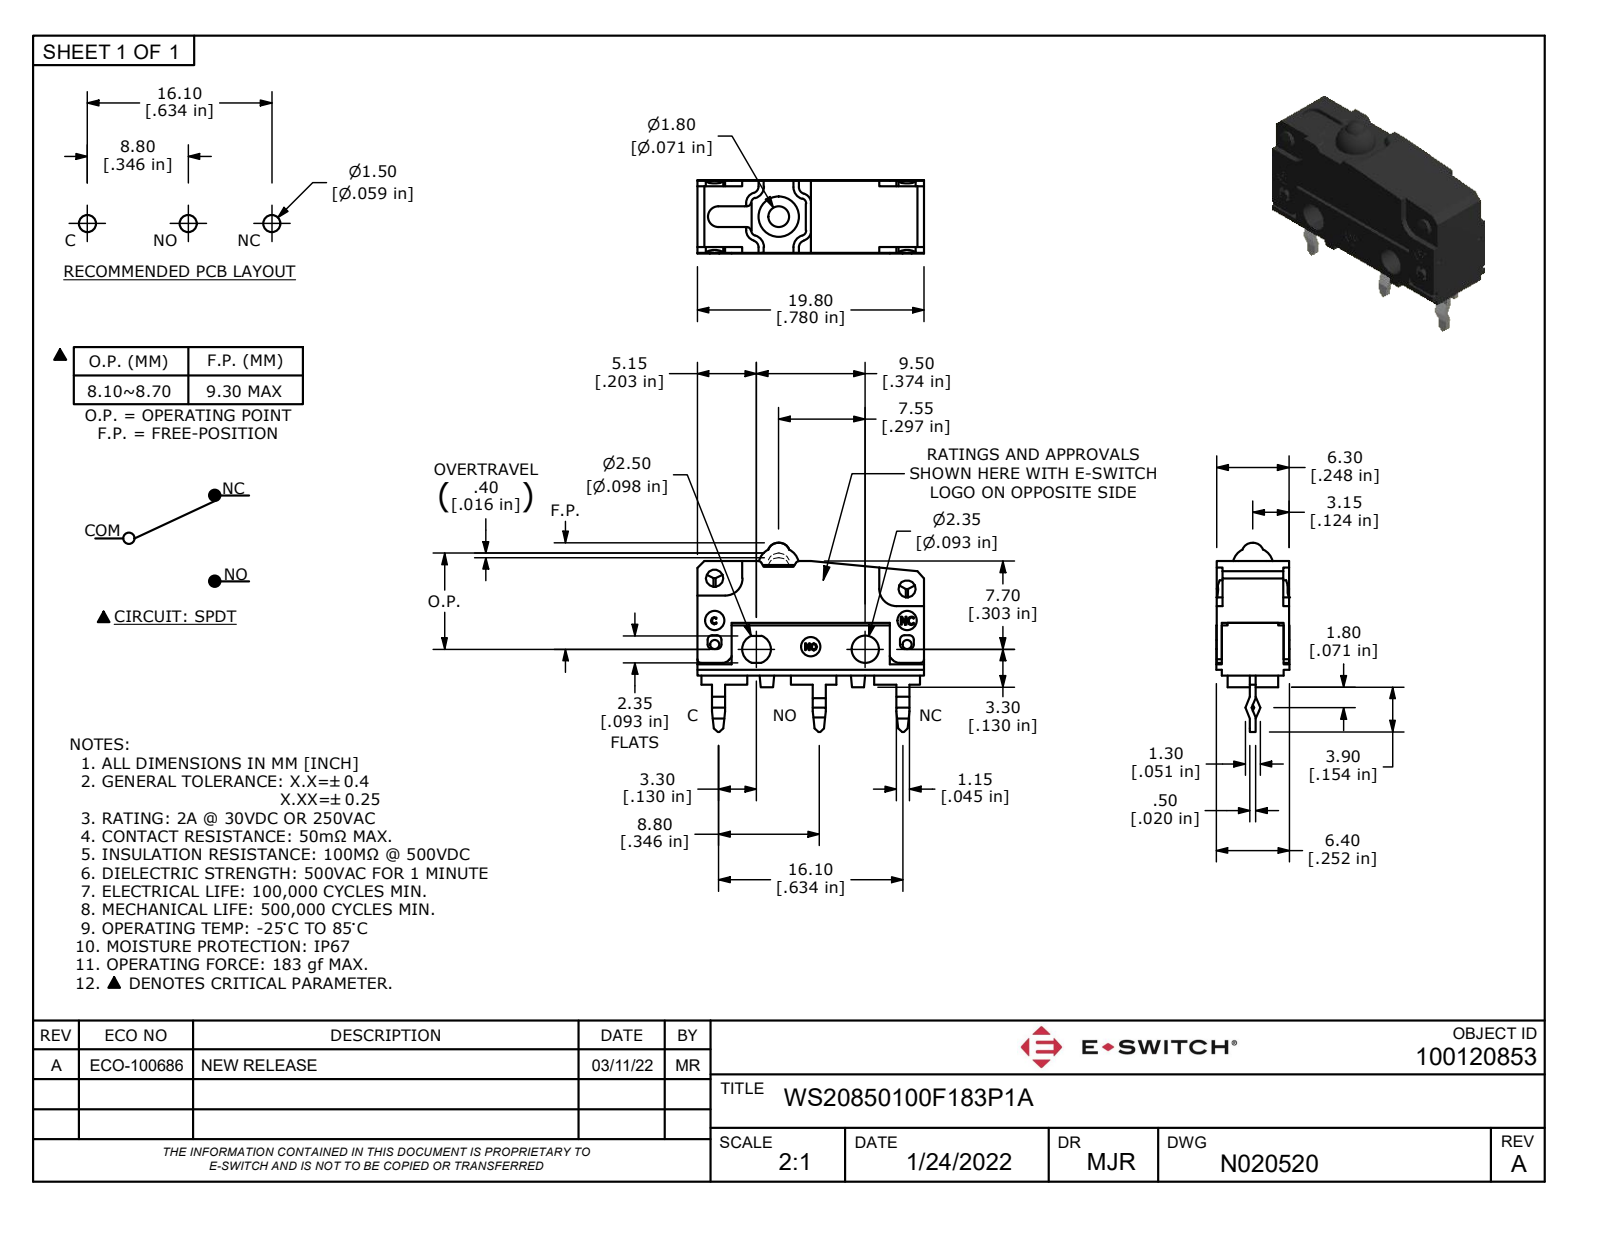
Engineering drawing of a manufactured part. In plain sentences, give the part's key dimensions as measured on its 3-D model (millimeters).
The part is named "WS20850100F183P1A". Its 3-D file was written by "Autodesk Inventor 2020 (AUTOMOTIVE_DESIGN)". It is 1 solid with 391 faces: 255 planar, 65 cylindrical and 71 other. Overall it measures 19.8 by 16.5 by 6.4 millimeters. Its volume is 1 141 cubic millimeters and its surface area 1 035 square millimeters. Round holes: 3 of diameter 1.7, 1 of diameter 2.35. Round bosses or shafts: 2 of diameter 1.5, 2 of diameter 0.8, 1 of diameter 3.5. Partial cylindrical surfaces (rounded edges, fillets, slot ends): 10 of radius 0.3, 8 of radius 0.4, 2 of radius 0.1, 2 of radius 0.8, 2 of radius 1.5, 1 of radius 0.9, 1 of radius 1.25. The main face-to-face distances are 0.5, 6.35, 6.3, 5.85, 2.9, 2.95, 19.8, 0.45, 6.4, 5.8. The hole center spacings are 8.71, 4.44, 4.76, 13.39, 16.8.
